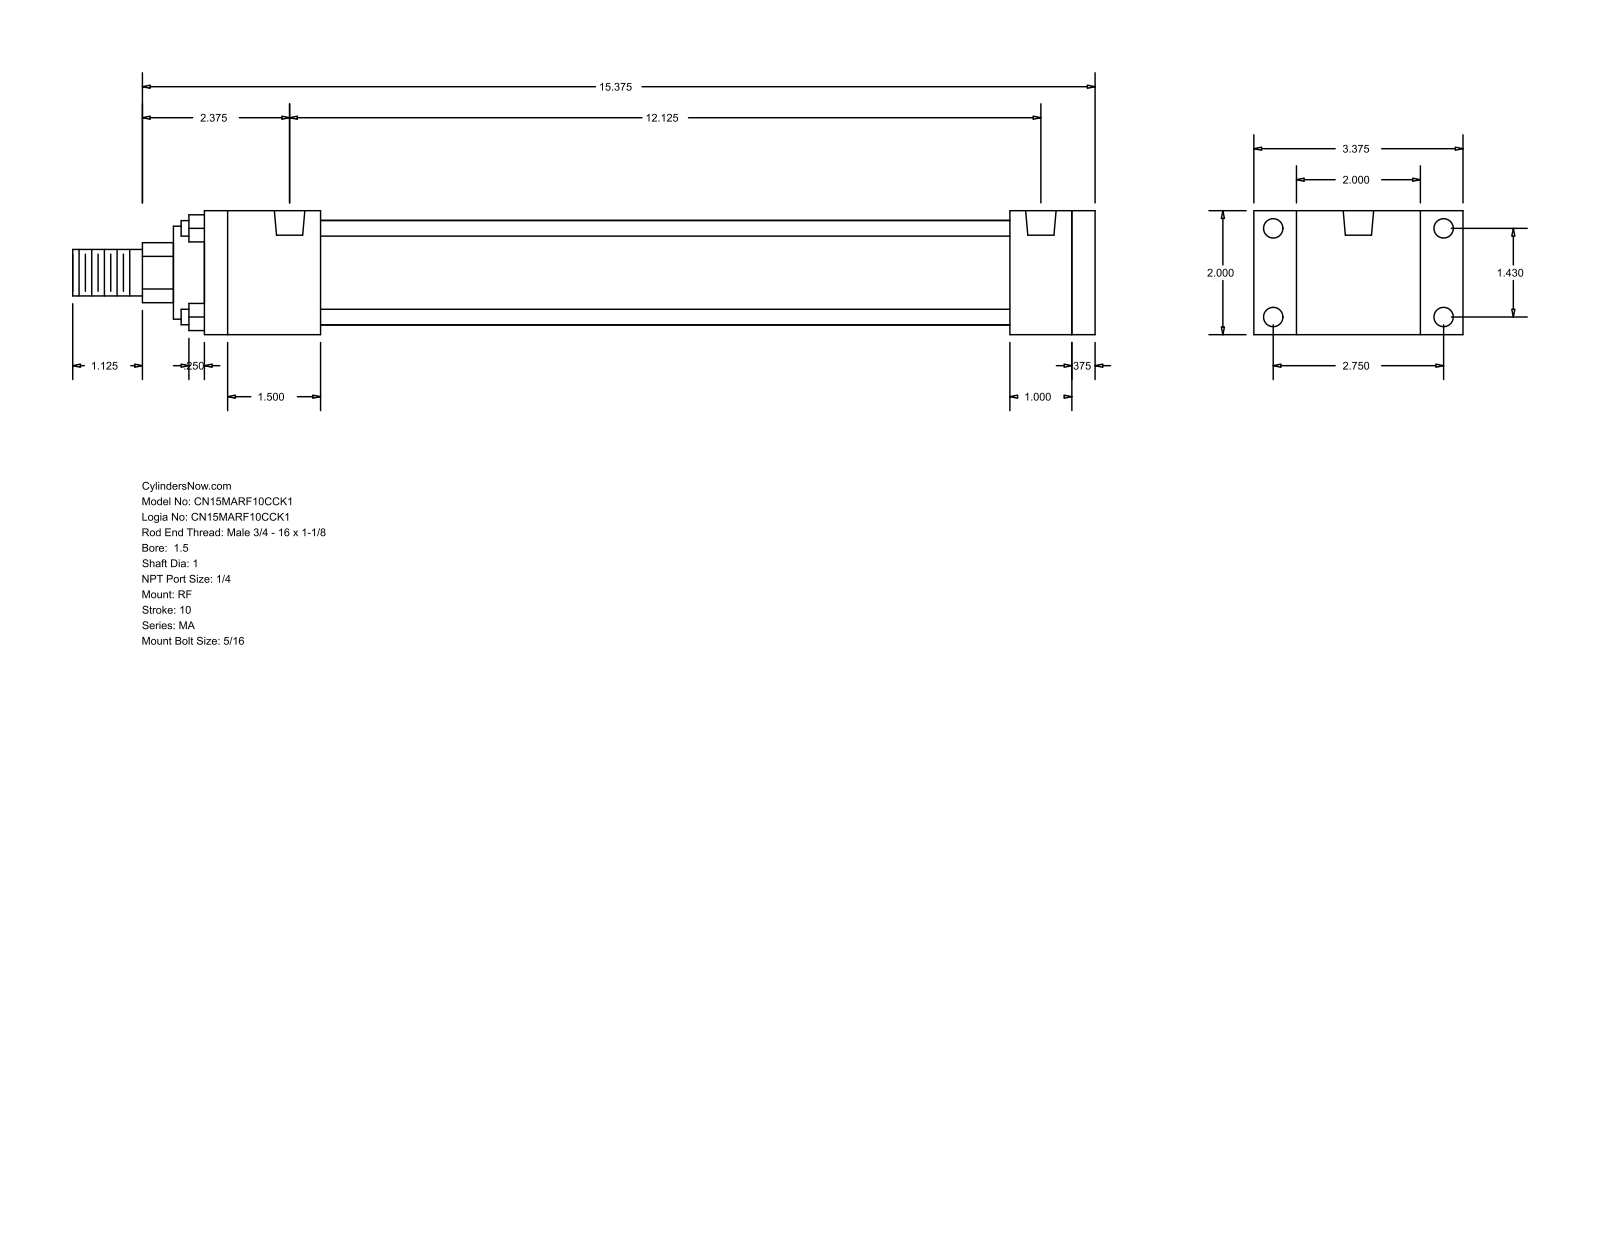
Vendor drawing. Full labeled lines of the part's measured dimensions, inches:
Part name (STEP PRODUCT): MA_RF__0150_1
STEP written by: GSSL Pune (CONFIG_CONTROL_DESIGN)
Units: inches
Bodies: 0 solids, 92 faces (64 planar, 28 cylindrical, 0 other)
Overall size (bounding box): 16.5 × 3.375 × 2
Round holes (diameter × count): ⌀0.313 ×8, ⌀0.492 ×2
Round bosses / shafts (diameter × count): ⌀0.25 ×4, ⌀1.69 ×1, ⌀1.5 ×1, ⌀1 ×1, ⌀0.75 ×1
Partial cylindrical surfaces — rounded edges, fillets, slot ends (radius × count): R0.484 ×1
Main face-to-face distances: 2, 0.375, 14.375, 14, 1, 13, 1.375, 1.875, 11.125, 12.125
Hole centre spacings: 1.43, 2.75, 3.099, 12.125
